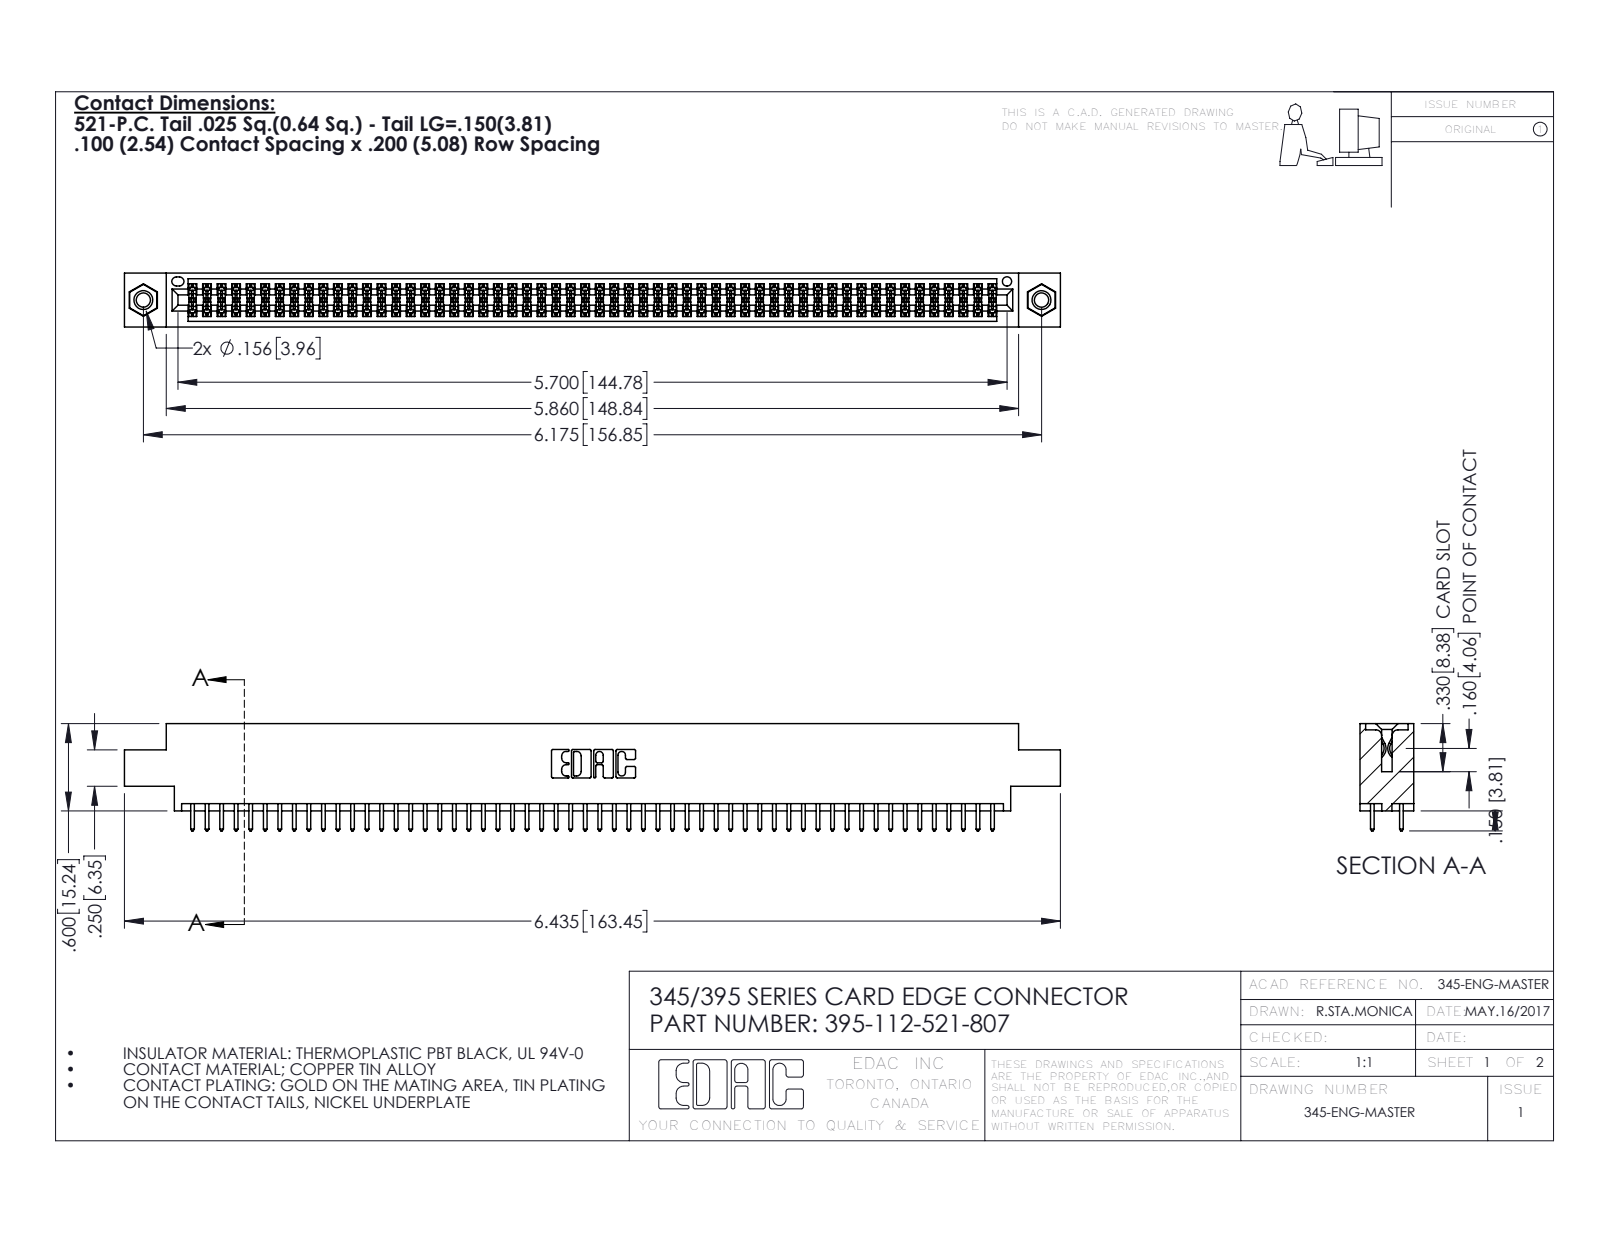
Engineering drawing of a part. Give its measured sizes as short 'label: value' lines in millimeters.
name: 345 Part_0.170 Offset - 0.156 Dia-TI; 345-250-001_345-250-005-103; 345-292-001_345-293-121; 395-112-521-807
written by: SolidWorks 2016 (CONFIG_CONTROL_DESIGN)
unit: mm
bodies: 115 solids, 5790 faces (3812 planar, 1962 cylindrical, 16 other)
size: 163.4 × 18.7 × 9.4
volume: 15 800 mm³; area: 23 550 mm²
holes: 2× ⌀2.5, 2× ⌀3.2, 2× ⌀4, 1× ⌀1.6
bosses: 2× ⌀3.9
rounds: 168× R0.2, 112× R0.3, 22× R0.3, 6× R0.2, 6× R0.8, 3× R0.7, 2× R0.4, 2× R0.5
face distances: 1.8, 7.6, 5.1, 9.4, 2.5, 6.9, 0.6, 5.7, 4.4, 3.8
hole spacings: 6.9, 150.9, 156.8
